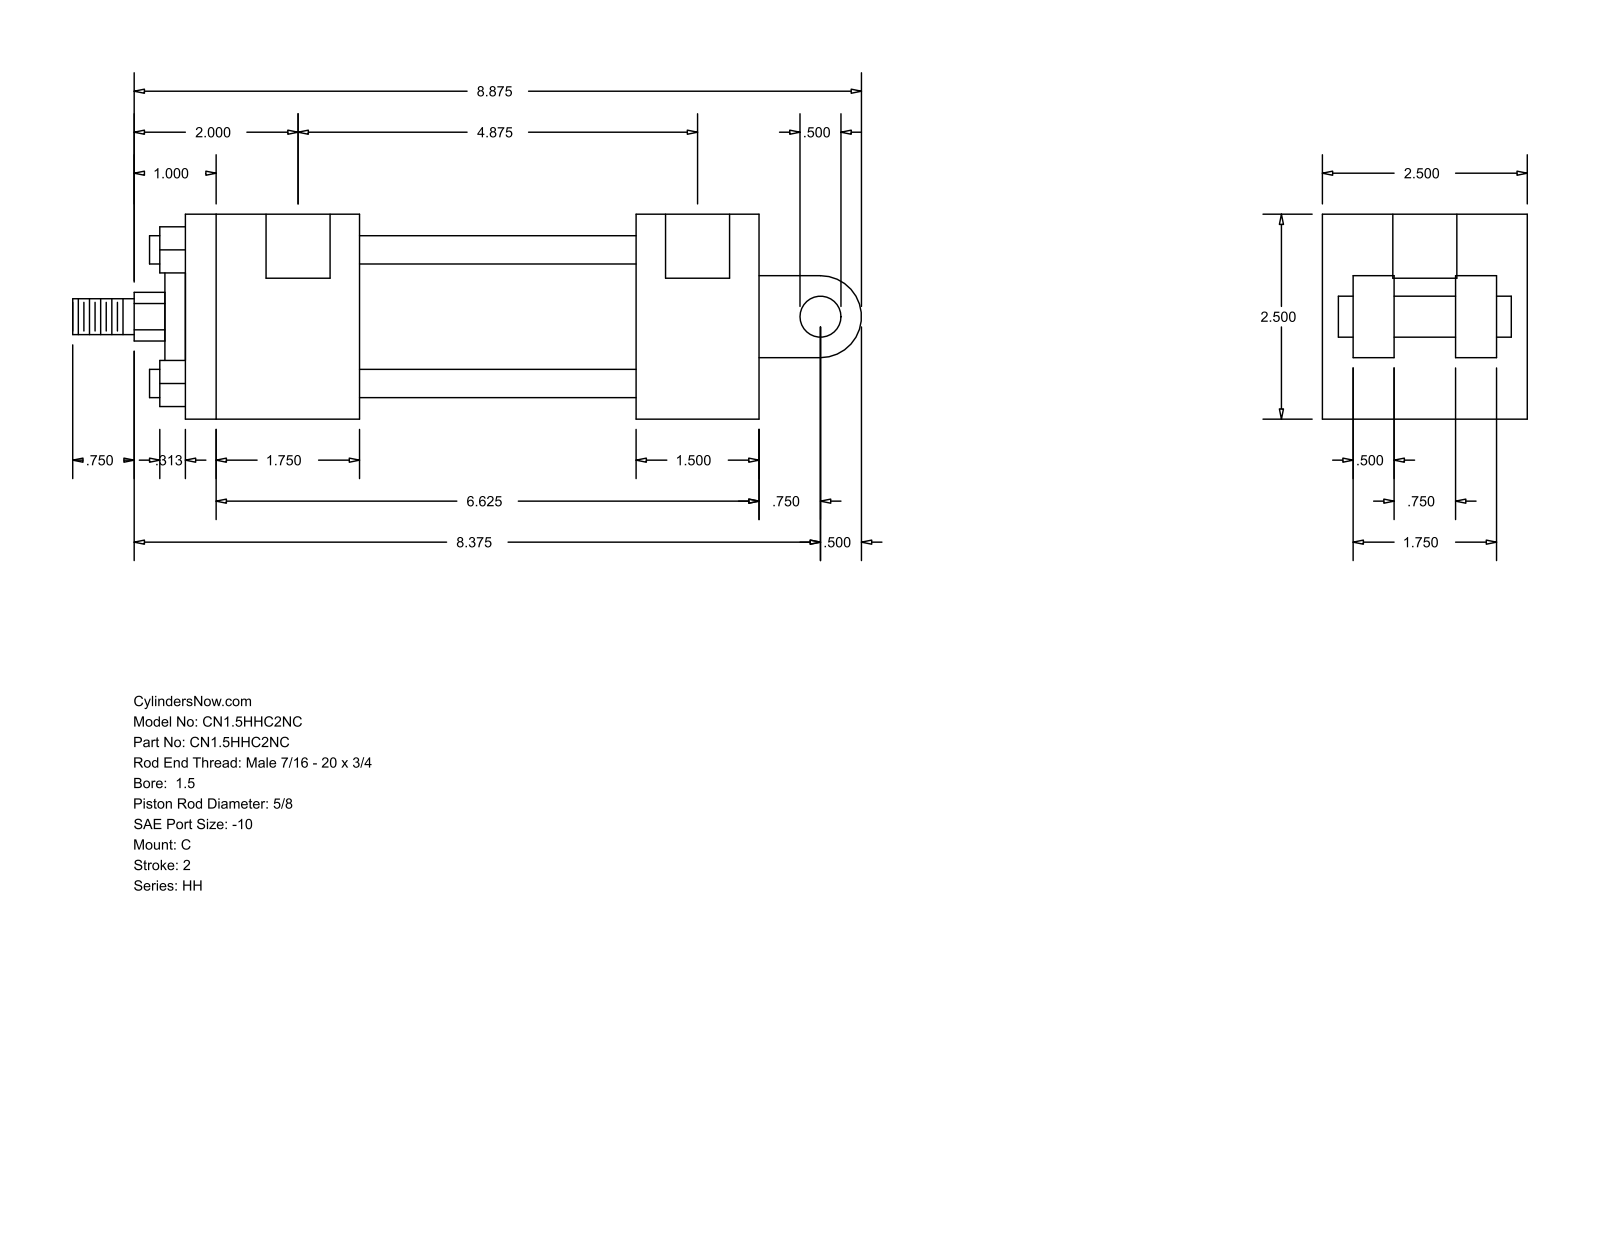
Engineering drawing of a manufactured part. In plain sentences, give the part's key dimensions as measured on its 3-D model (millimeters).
The part is named "HH_C__0150_0.625". Its 3-D file was written by "GSSL Pune (CONFIG_CONTROL_DESIGN)". It is 0 solids with 99 faces: 70 planar, 29 cylindrical and 0 other. Overall it measures 244.47 by 63.5 by 63.5 millimeters. Round holes: 4 of diameter 5.56, 2 of diameter 19.84. Round bosses or shafts: 4 of diameter 8.76, 1 of diameter 44.45, 1 of diameter 28.57, 1 of diameter 15.88, 1 of diameter 12.7, 1 of diameter 11.11. Partial cylindrical surfaces (rounded edges, fillets, slot ends): 1 of radius 7.54, 1 of radius 12.7. The main face-to-face distances are 63.5, 177.8, 53.97, 139.69, 85.72, 123.83, 38.11, 12.7, 19.05, 9.52. The hole center spacings are 1.59, 125.41, 127, 123.82.
